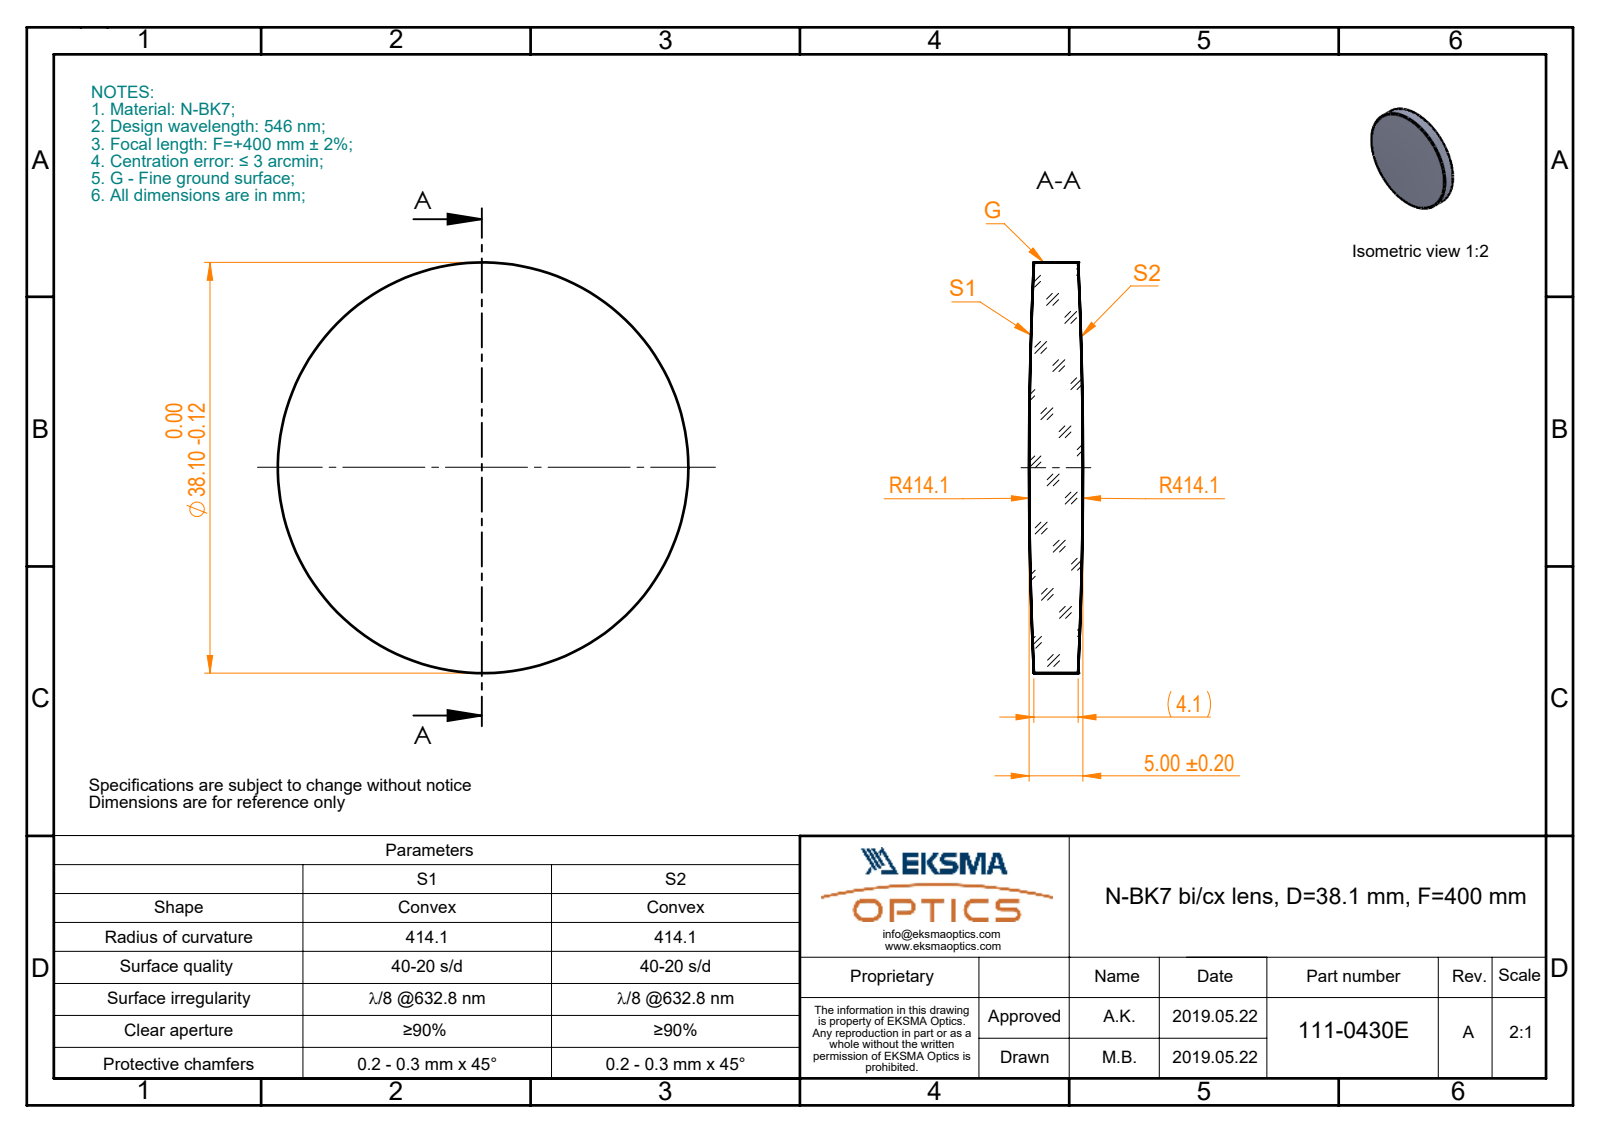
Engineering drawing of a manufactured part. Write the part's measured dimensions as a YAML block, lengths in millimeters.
part_name: "111-0430E BK7 bi-cx 38.1 F400"
step_written_by: "SolidWorks 2017 (CONFIG_CONTROL_DESIGN)"
units: millimeters
bodies: {solids: 1, faces: 6, planar: 0, cylindrical: 2, other: 4}
overall_size: [38.1, 38.1, 5]
volume: 5034
surface_area: 2741
round_bosses_or_shafts:
  - {diameter: 38.1, count: 1}
